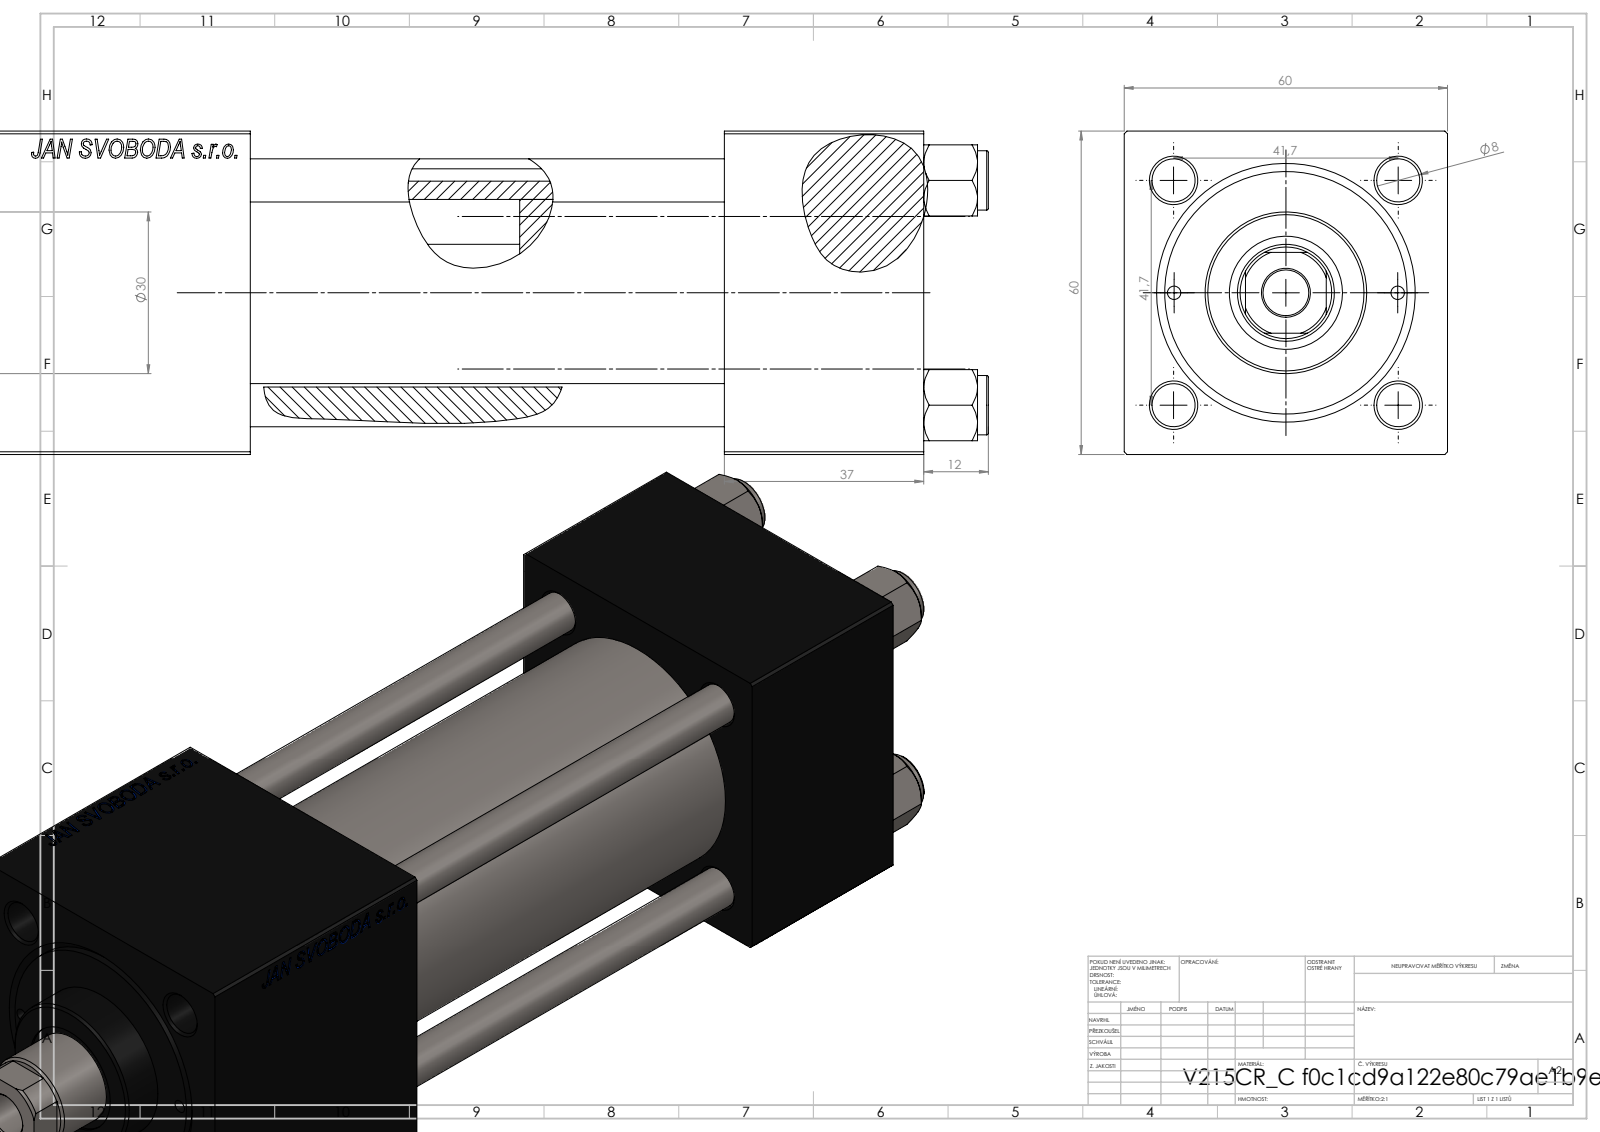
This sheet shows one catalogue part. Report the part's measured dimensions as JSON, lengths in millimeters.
{"part_name": "NUT_M5_C; V215CR_C_Body; V215CR_VCP_C; V215CR_C_TYCINKA (+1 more)", "step_written_by": "SolidWorks 2019 (CONFIG_CONTROL_DESIGN)", "units": "millimeters", "bodies": {"solids": 11, "faces": 1154, "planar": 528, "cylindrical": 90, "other": 536}, "overall_size": [215, 60, 60], "volume_mm3": 428343, "surface_area_mm2": 118225, "round_holes": [[8, 4], [2.5, 2], [7, 2], [16.66, 2], [24, 2], [8.5, 1], [18, 1], [21, 1], [31, 1], [40, 1], [45, 1]], "round_bosses_or_shafts": [[11, 4], [46, 1], [30, 1]], "partial_cylinders_radius": [[8.5, 1]], "face_to_face_distances": [60, 37, 178, 141, 53, 125, 88, 149.3, 112.3, 24.3], "hole_center_spacings": [20.85, 29.49, 41.7, 46.53, 20.75, 58.97, 41.5, 122.5]}
